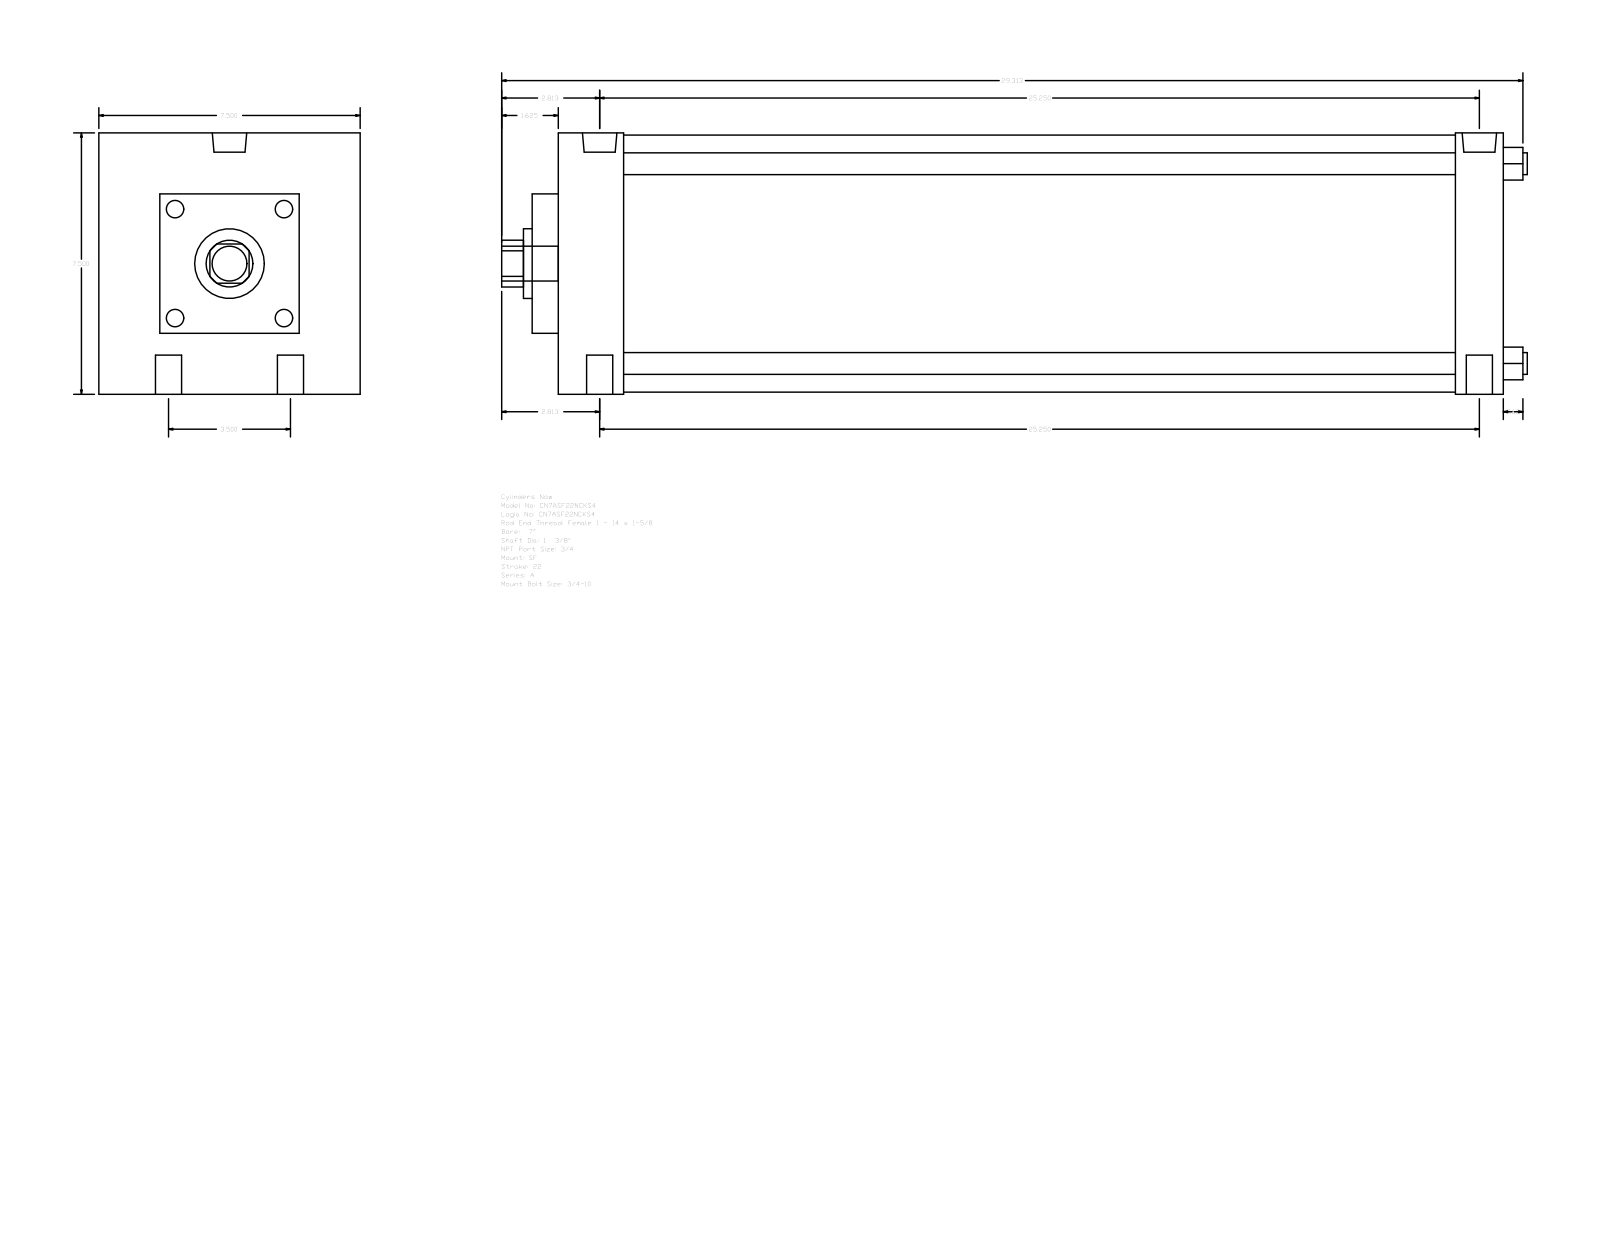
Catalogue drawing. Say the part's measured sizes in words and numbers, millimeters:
The part is named "A_SF__0700_1.375". Its 3-D file was written by "GSSL Pune (CONFIG_CONTROL_DESIGN)". It is 0 solids with 93 faces: 67 planar, 26 cylindrical and 0 other. Overall it measures 747.71 by 190.5 by 190.5 millimeters. Round holes: 4 of diameter 19.05, 2 of diameter 15.08, 2 of diameter 25.12, 1 of diameter 34.92, 1 of diameter 50.8. Round bosses or shafts: 4 of diameter 15.88, 1 of diameter 187.32, 1 of diameter 25.4. Partial cylindrical surfaces (rounded edges, fillets, slot ends): 1 of radius 17.06. The main face-to-face distances are 190.5, 688.98, 19.04, 708.02, 66.67, 673.1, 47.63, 654.06, 606.43, 641.35. The hole center spacings are 44.45, 642.89, 641.35, 88.9, 647.48, 630.23.
